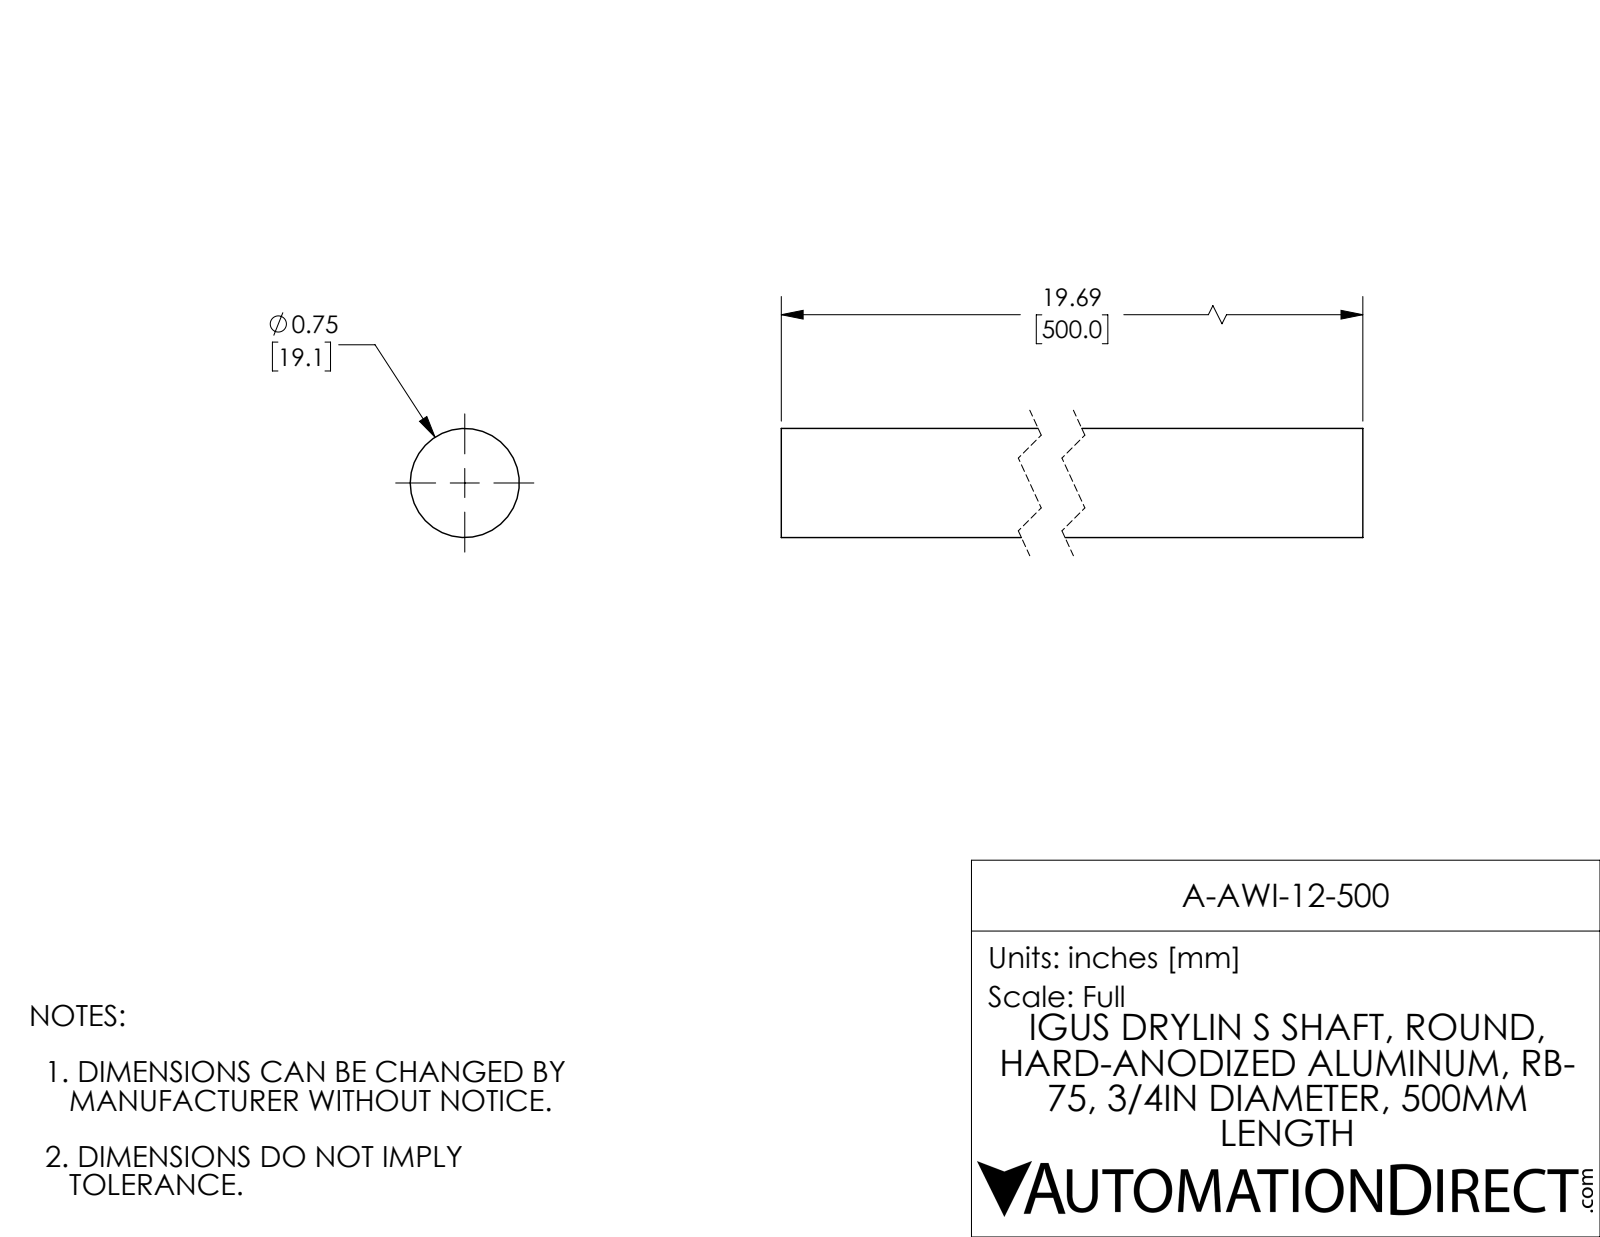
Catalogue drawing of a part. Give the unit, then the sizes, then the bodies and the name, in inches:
Units: inches
Overall size (bounding box): 19.685 × 0.75 × 0.75
Round bosses / shafts (diameter × count): ⌀0.75 ×1
Main face-to-face distances: 19.685
Volume: 8.697 in³ · Surface area: 47.27 in²
Bodies: 1 solid, 4 faces (2 planar, 2 cylindrical, 0 other)
Part name (STEP PRODUCT): A-AWI-12-500
STEP written by: SolidWorks 2017 (AUTOMOTIVE_DESIGN)
